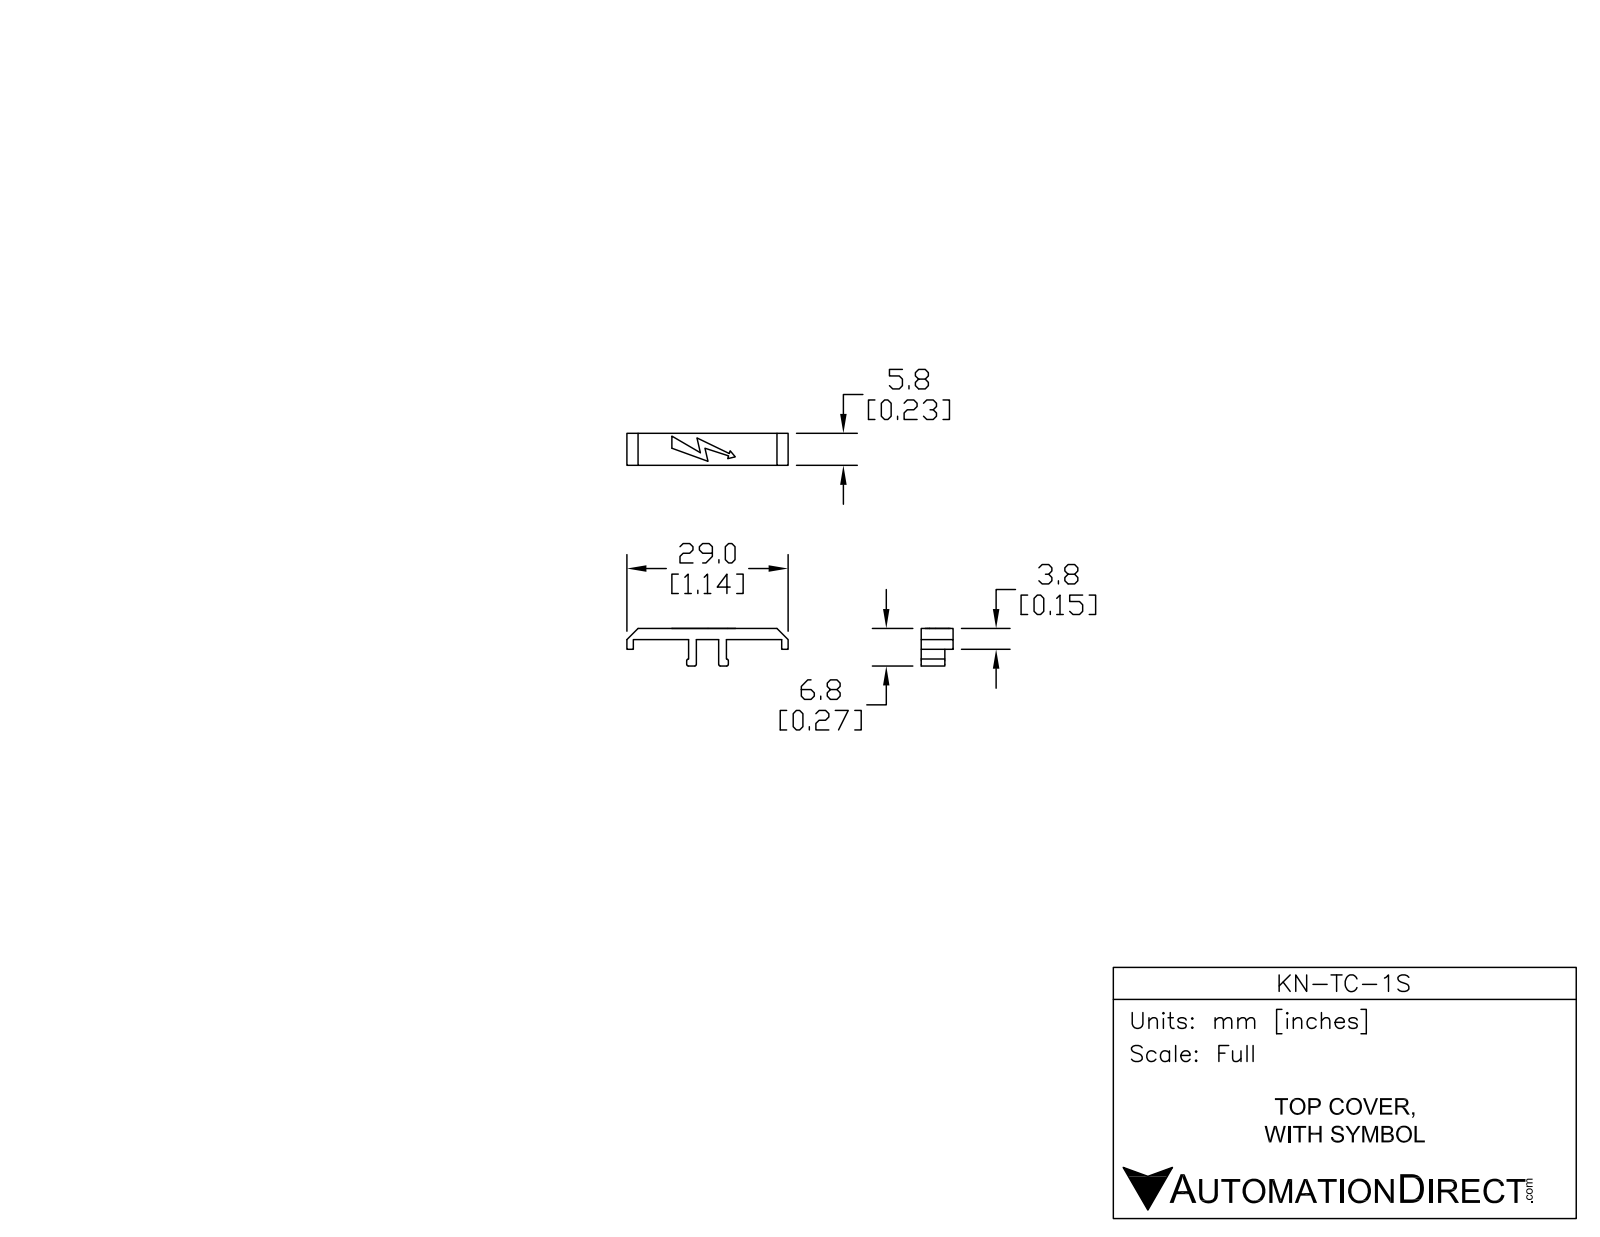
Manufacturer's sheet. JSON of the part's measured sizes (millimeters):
{"part_name": "KN-TC-1S", "step_written_by": "SolidWorks 2014 (AUTOMOTIVE_DESIGN)", "units": "millimeters", "bodies": {"solids": 1, "faces": 42, "planar": 36, "cylindrical": 6, "other": 0}, "overall_size": [29, 6.76, 5.75], "volume_mm3": 394, "surface_area_mm2": 611, "partial_cylinders_radius": [[0.3, 6]], "face_to_face_distances": [2, 5.75, 1.4, 5.4, 11.1, 12.5, 16.5, 17.9, 1.15, 27.85]}
